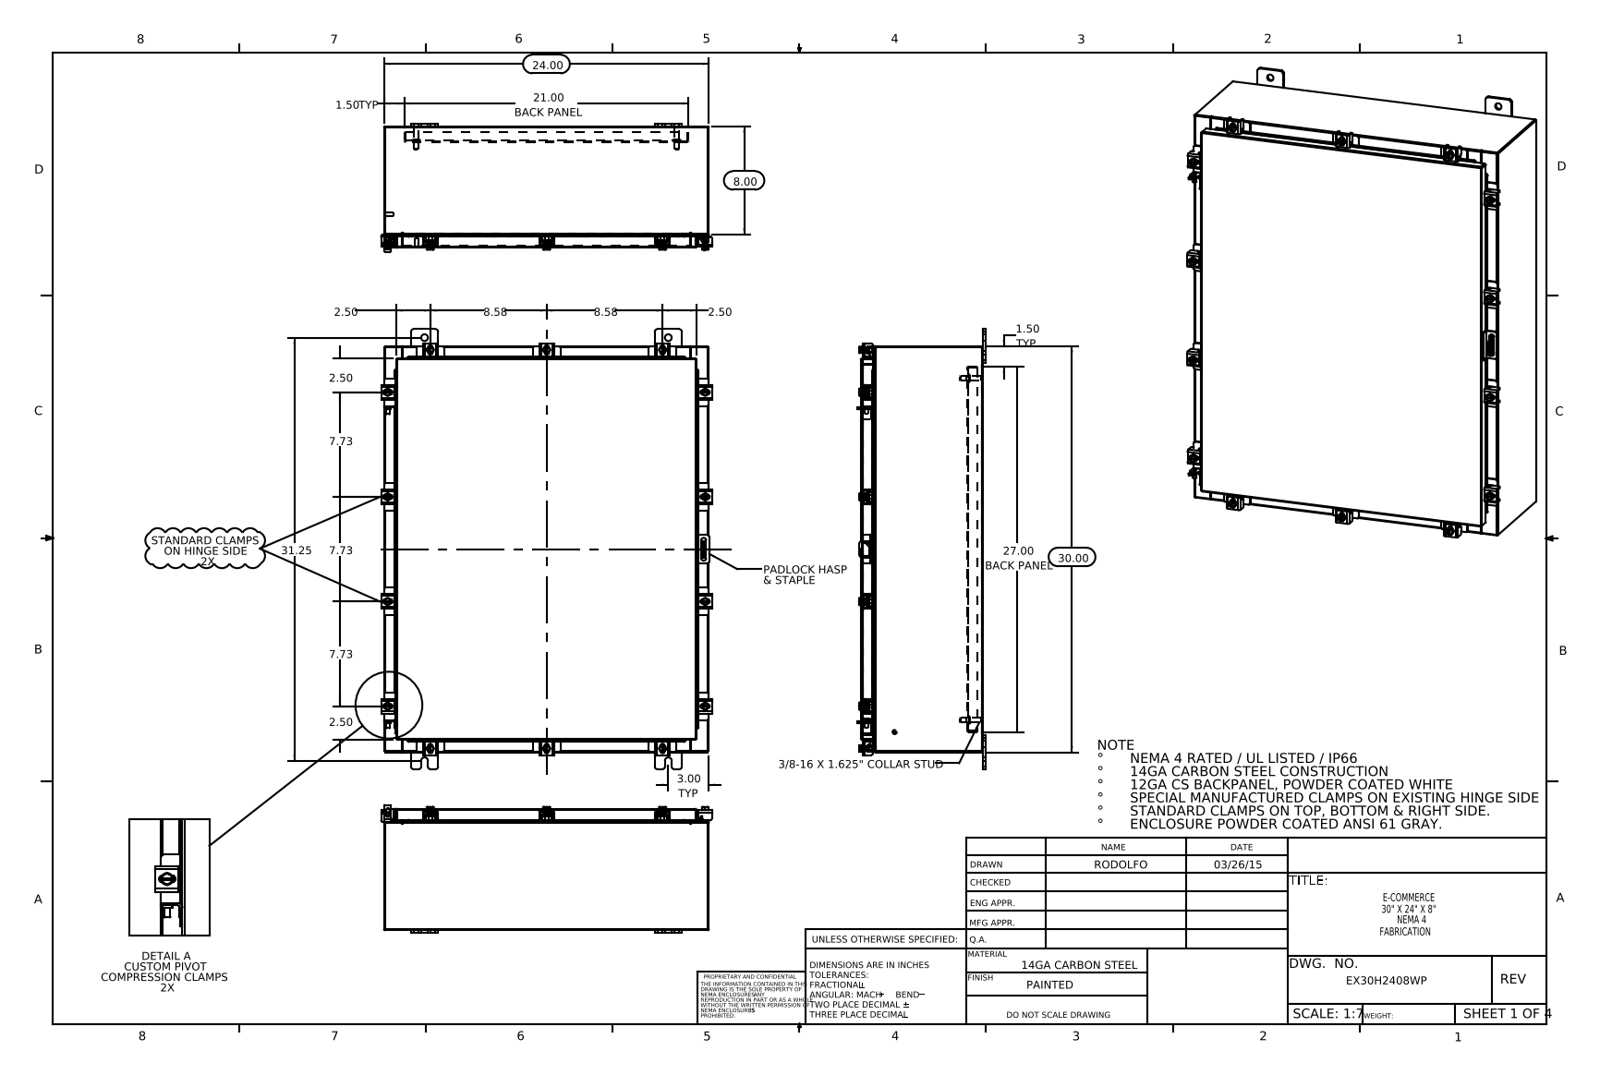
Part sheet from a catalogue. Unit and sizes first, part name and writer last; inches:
Units: inches
Overall size (bounding box): 32.5 × 24.421 × 9.453
Round holes (diameter × count): ⌀0.213 ×14, ⌀0.26 ×14, ⌀0.5 ×8, ⌀0.125 ×1, ⌀0.25 ×1
Round bosses / shafts (diameter × count): ⌀0.5 ×14, ⌀0.25 ×14, ⌀0.399 ×12, ⌀0.625 ×4, ⌀0.375 ×4, ⌀0.33 ×4, ⌀0.315 ×2, ⌀0.236 ×2
Partial cylindrical surfaces — rounded edges, fillets, slot ends (radius × count): R0.06 ×62, R0.141 ×28, R0.013 ×26, R0.12 ×26, R0.19 ×24, R0.088 ×22, R0.09 ×20, R0.05 ×19
Main face-to-face distances: 0.075, 8.9, 8.975, 8.826, 0.104, 1, 1.075, 7.826, 7.9, 1.179
Hole centre spacings: 2.347, 4.44, 20.544, 23.451, 24.31, 26.507, 27.37, 32.286
Volume: 264.6 in³ · Surface area: 6 573 in²
Bodies: 91 solids, 2272 faces (1211 planar, 885 cylindrical, 176 other)
Part name (STEP PRODUCT): EX30H2408WP Standard Clamps; 22101002_RTP29; EX30H2408WP Top; 22104005_DEFAULT_RTP30 (+8 more)
STEP written by: SolidWorks 2014 (CONFIG_CONTROL_DESIGN)
